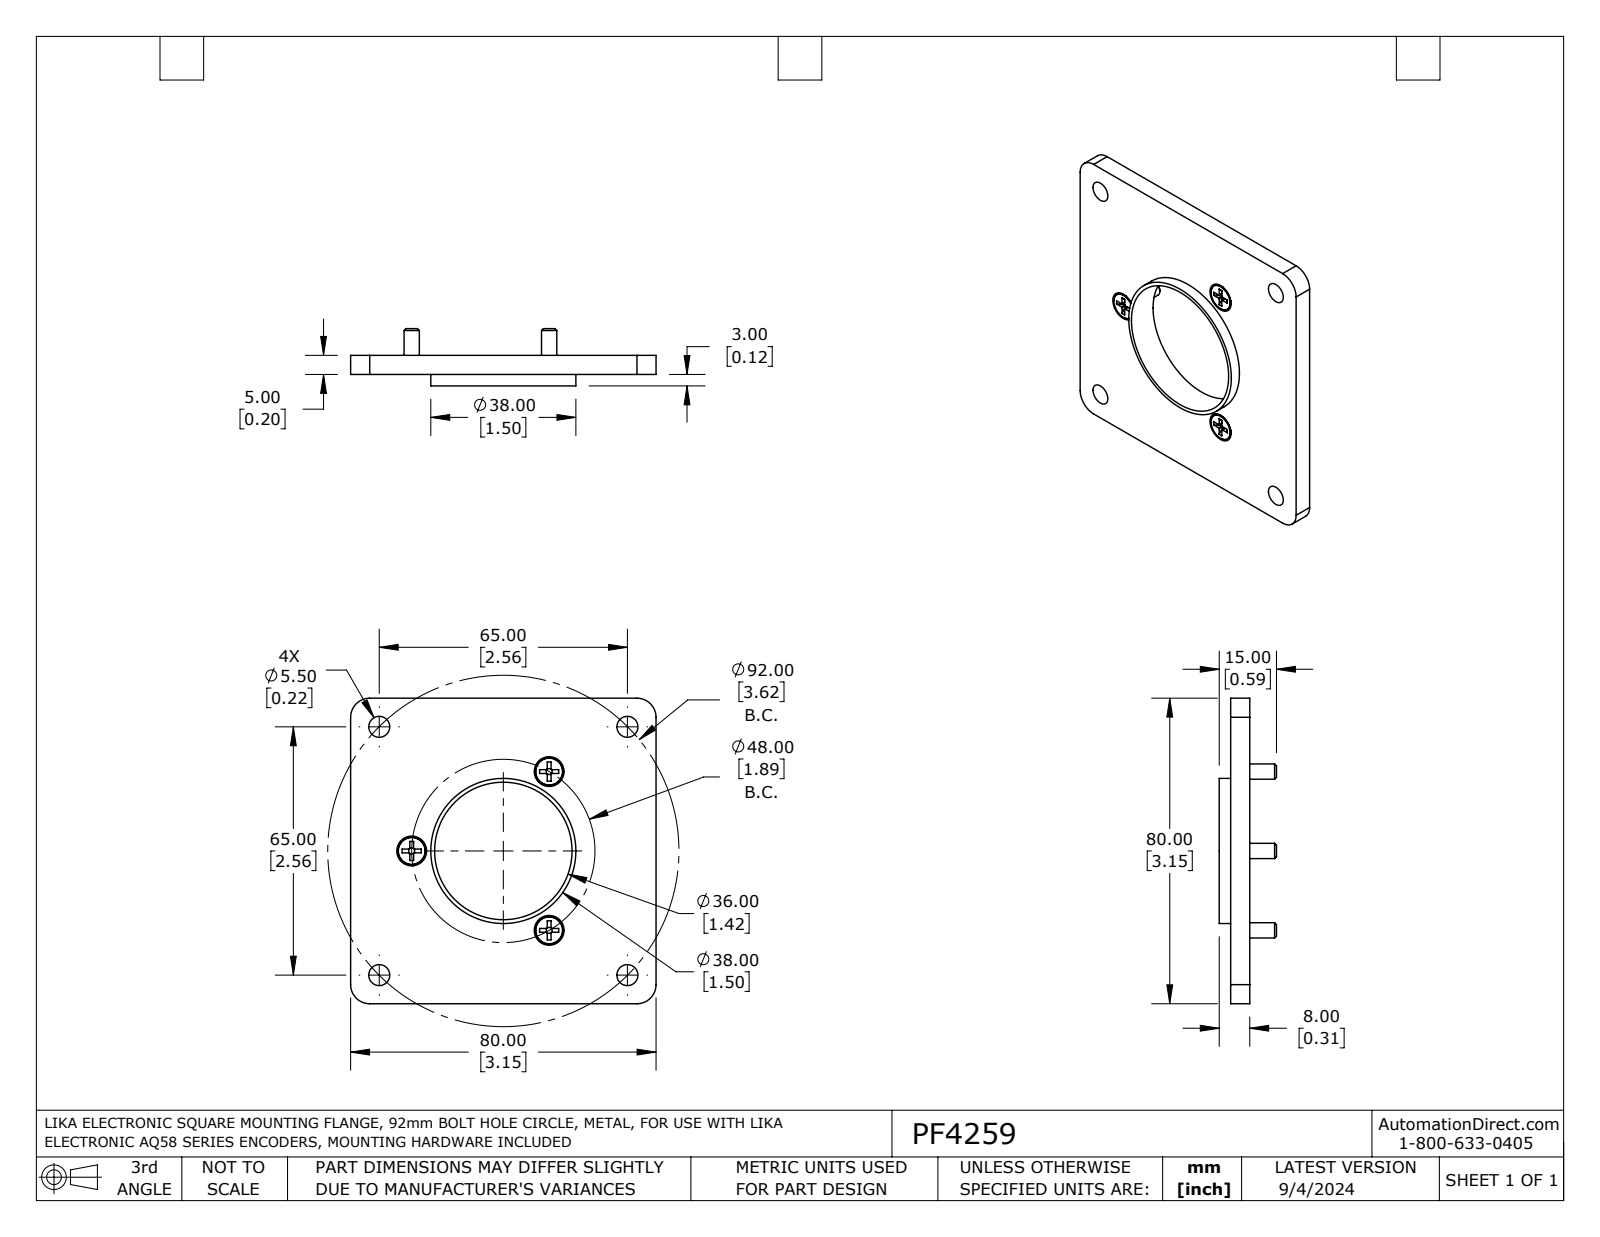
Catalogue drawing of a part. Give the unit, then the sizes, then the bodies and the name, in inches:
Units: inches
Overall size (bounding box): 3.15 × 3.15 × 0.591
Round holes (diameter × count): ⌀0.217 ×4, ⌀0.169 ×3, ⌀1.417 ×1
Round bosses / shafts (diameter × count): ⌀0.157 ×3, ⌀1.496 ×1
Partial cylindrical surfaces — rounded edges, fillets, slot ends (radius × count): R0.007 ×9, R0.197 ×4, R0.008 ×3
Main face-to-face distances: 0.197, 3.15, 0.315, 0.118, 0.276, 0.472, 0.591, 0.039, 0.818, 0.415
Hole centre spacings: 1.809, 2.559, 0.945, 0.93, 1.322, 1.637, 1.812, 2.248
Volume: 1.639 in³ · Surface area: 22.46 in²
Bodies: 4 solids, 122 faces (52 planar, 40 cylindrical, 30 other)
Part name (STEP PRODUCT): PF4259
STEP written by: SolidWorks 2021 (AUTOMOTIVE_DESIGN)
